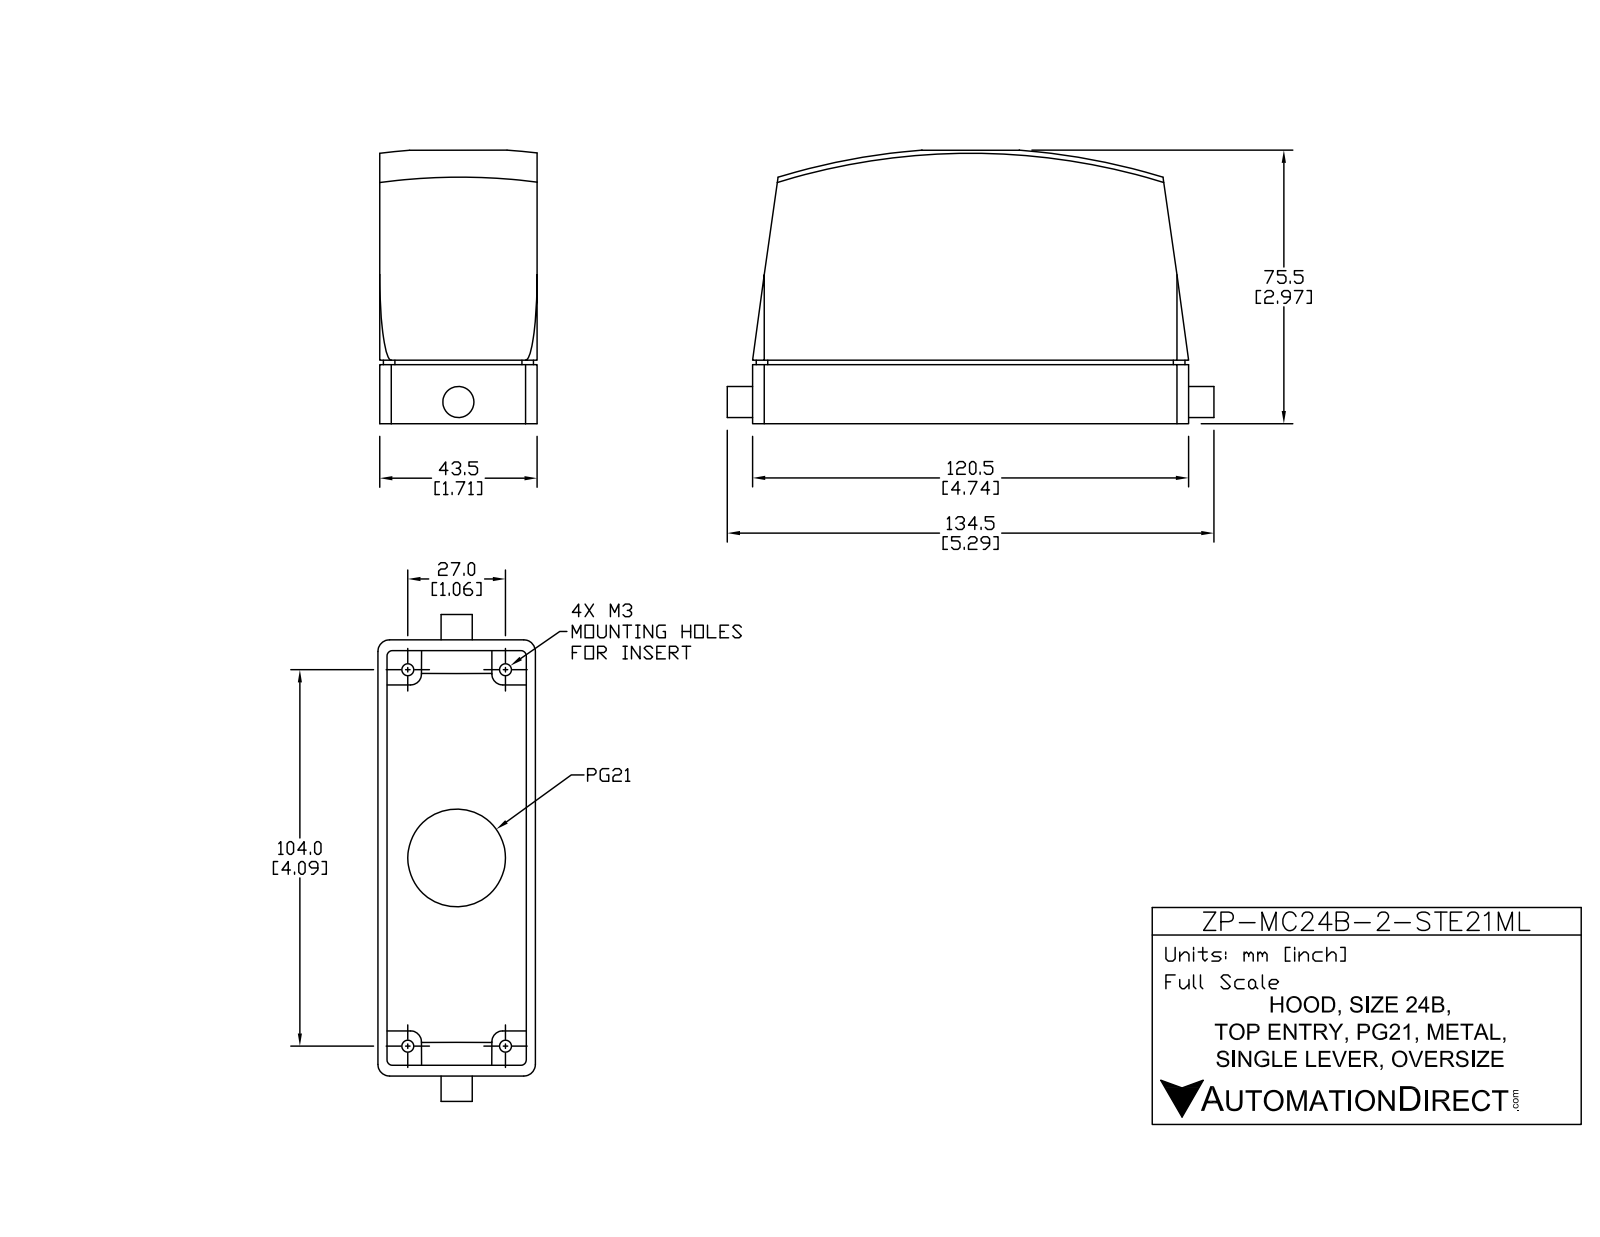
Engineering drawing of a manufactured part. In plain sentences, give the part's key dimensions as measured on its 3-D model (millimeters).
The part is named "ZP-MC24B-2-STE21ML". Its 3-D file was written by "SolidWorks 2011 (AUTOMOTIVE_DESIGN)". It is 5 solids with 86 faces: 52 planar, 28 cylindrical and 6 other. Overall it measures 134.5 by 77.08 by 43.5 millimeters. Its volume is 79 881 cubic millimeters and its surface area 61 596 square millimeters. Round holes: 4 of diameter 3.5, 1 of diameter 27. Round bosses or shafts: 1 of diameter 8.6. Partial cylindrical surfaces (rounded edges, fillets, slot ends): 8 of radius 3.2, 4 of radius 1.5, 4 of radius 3, 1 of radius 0.7. The main face-to-face distances are 2.5, 41, 43.5, 38.5, 9.5, 105.08, 2.96, 12.46, 108.04, 117.54. The hole center spacings are 53.72, 27, 104, 107.45.
